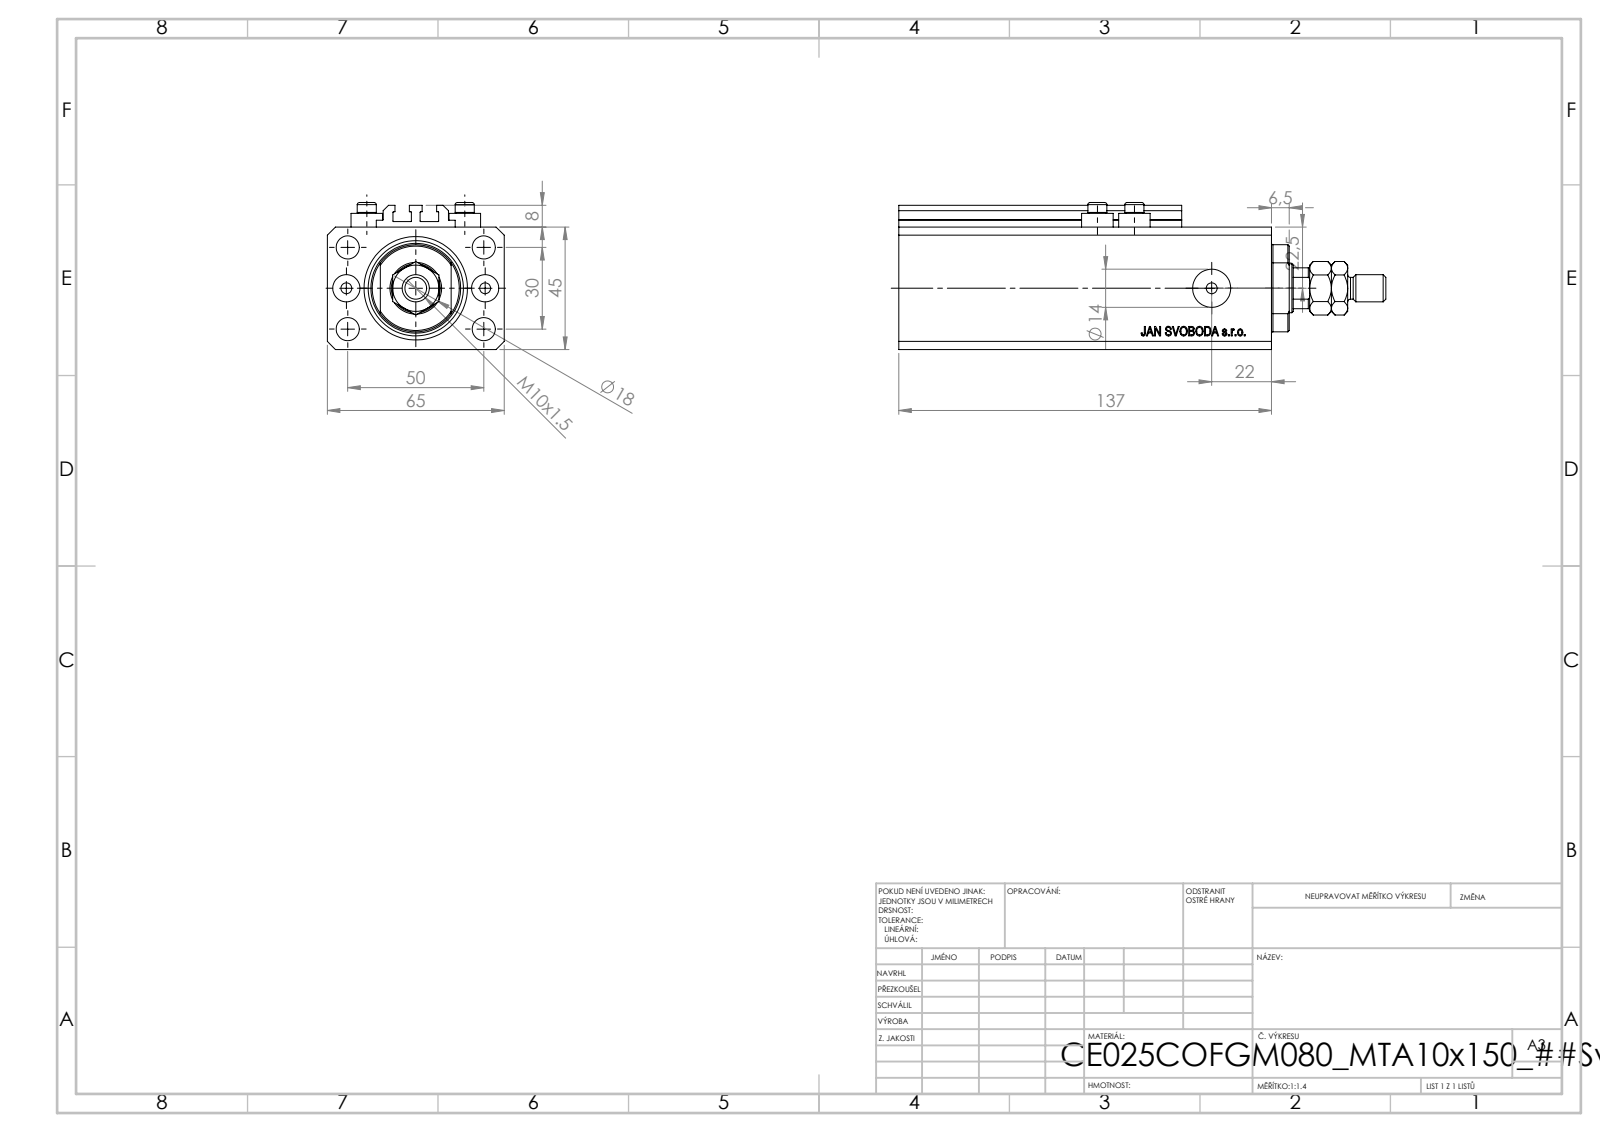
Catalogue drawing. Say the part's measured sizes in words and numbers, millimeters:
The part is named "V250CE_C_Body; V250CE_VC_C; MTA; ALLEN BOLT V250CE (+1 more)". Its 3-D file was written by "SolidWorks 2019 (CONFIG_CONTROL_DESIGN)". It is 9 solids with 1083 faces: 519 planar, 90 cylindrical and 474 other. Overall it measures 179 by 65 by 54 millimeters. Its volume is 370 613 cubic millimeters and its surface area 92 344 square millimeters. Round holes: 8 of diameter 4, 5 of diameter 8.5, 2 of diameter 10, 2 of diameter 14, 1 of diameter 18, 1 of diameter 25, 1 of diameter 38. Round bosses or shafts: 4 of diameter 11.6, 4 of diameter 7, 1 of diameter 10, 1 of diameter 8. Partial cylindrical surfaces (rounded edges, fillets, slot ends): 10 of radius 0.2, 1 of radius 8.5, 1 of radius 16. The main face-to-face distances are 45, 65, 14, 47, 123, 137, 2.5, 2, 6, 10. The hole center spacings are 15.01, 29.15, 52.68, 13.6, 25.5, 30, 36, 38.48.
